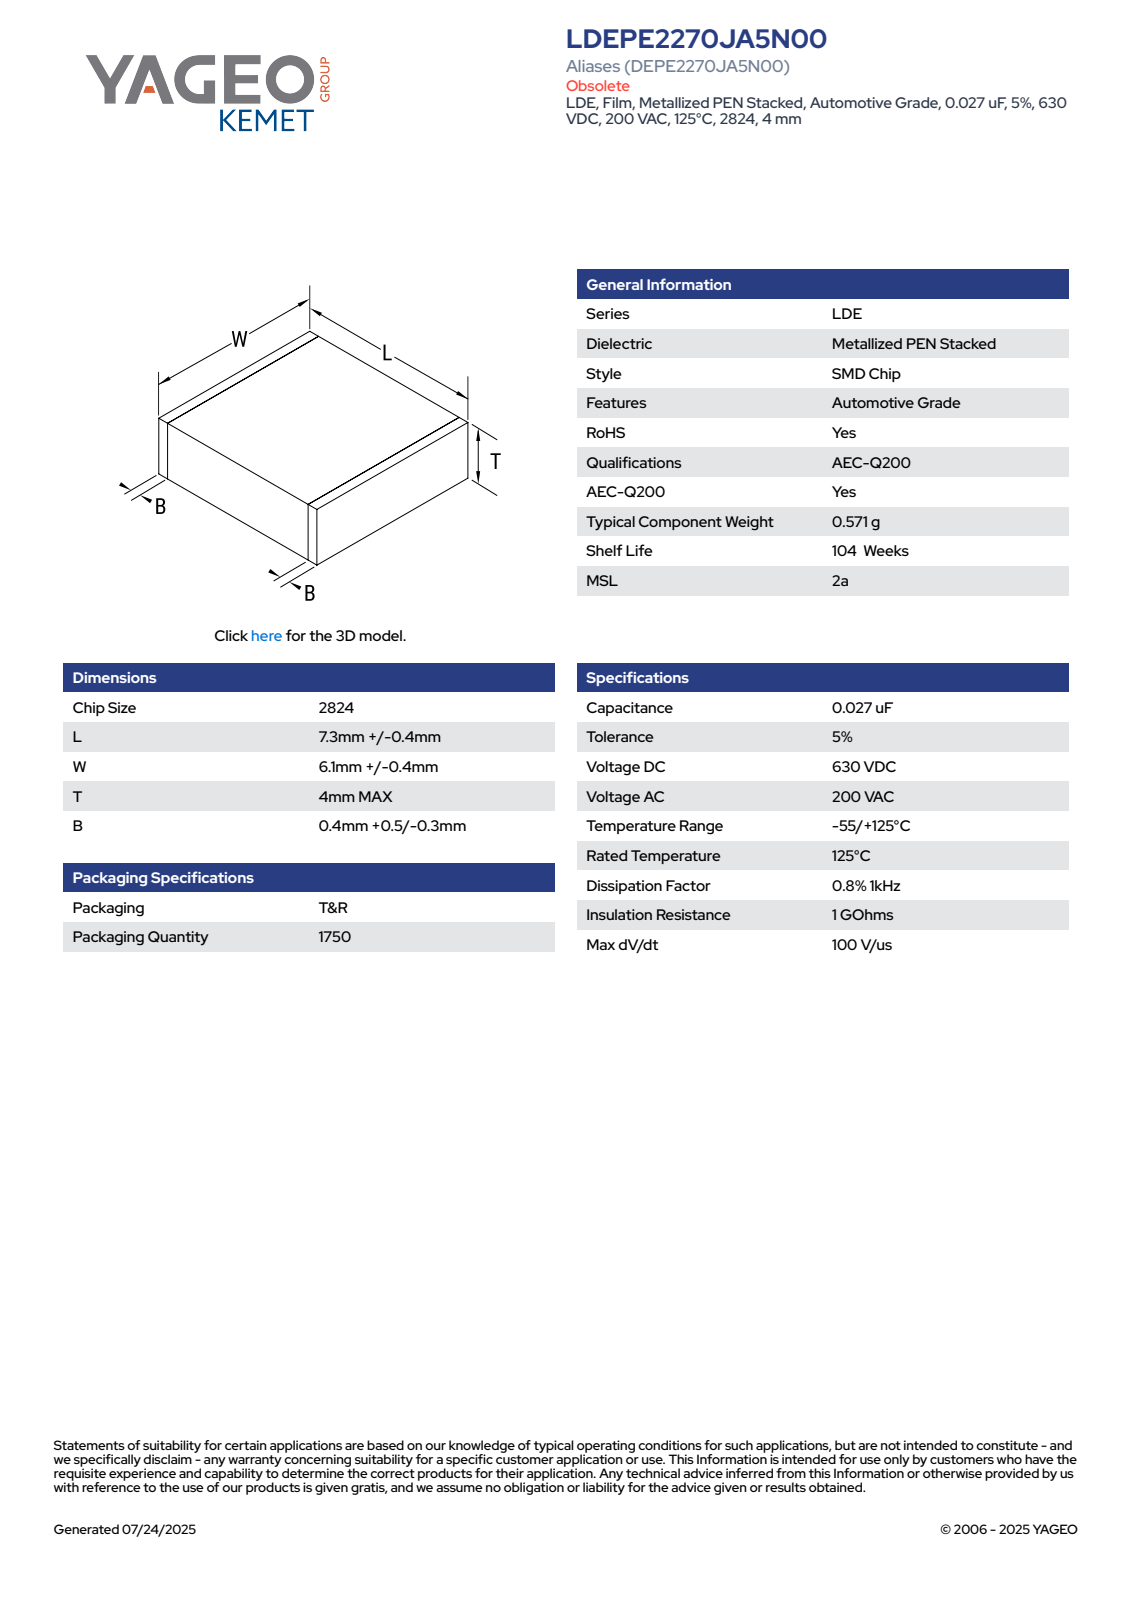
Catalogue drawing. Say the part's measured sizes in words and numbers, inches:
The part is named "CFS_LDELDB_2824_L7.7W6.5T4B0.9". Its 3-D file was written by "SolidWorks 2020 (AUTOMOTIVE_DESIGN)". It is 4 solids with 73 faces: 73 planar, 0 cylindrical and 0 other. Overall it measures 0.303 by 0.256 by 0.157 inches. Its volume is 0.012 cubic inches and its surface area 0.335 square inches. The main face-to-face distances are 0.157, 0.255, 0.303, 0.157, 0.256, 0.157, 0.256, 0.02, 0.283, 0.264.
